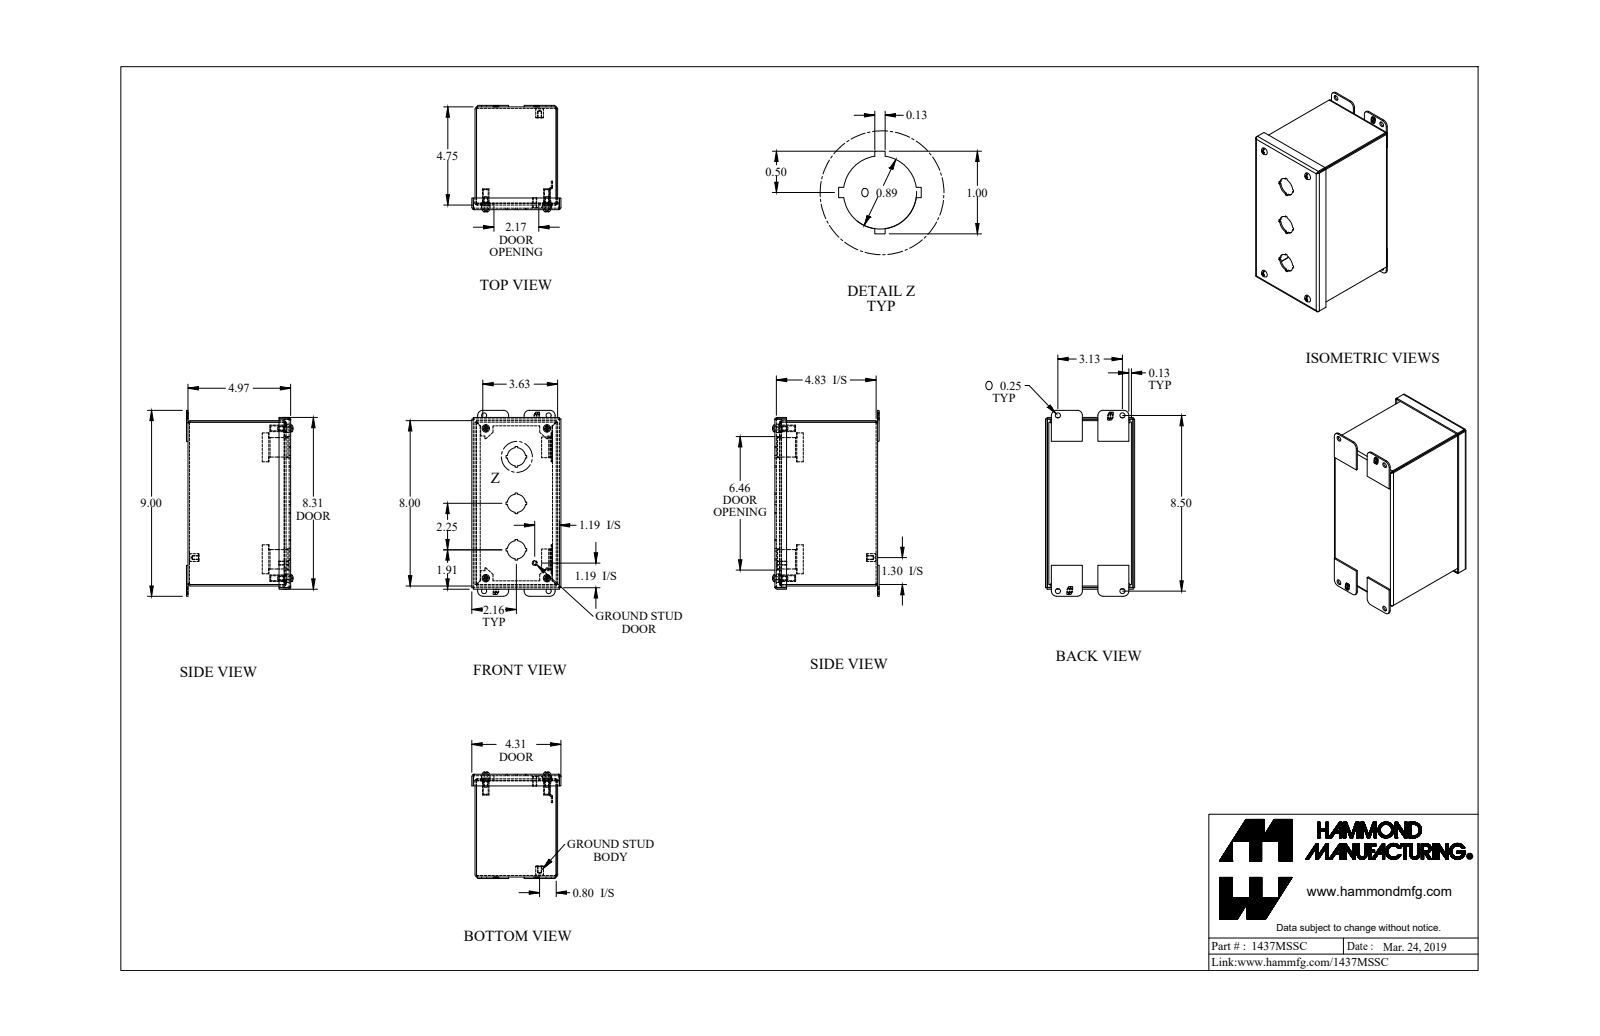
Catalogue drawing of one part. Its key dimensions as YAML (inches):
part_name: "1437MSSC_Default"
step_written_by: "SolidWorks 2019 (CONFIG_CONTROL_DESIGN)"
units: inches
bodies: {solids: 23, faces: 653, planar: 459, cylindrical: 164, other: 30}
overall_size: [9, 5.154, 4.312]
volume: 17.1
surface_area: 458
round_holes:
  - {diameter: 0.25, count: 8}
  - {diameter: 0.065, count: 4}
  - {diameter: 0.239, count: 4}
  - {diameter: 0.253, count: 4}
  - {diameter: 0.406, count: 4}
  - {diameter: 0.886, count: 3}
  - {diameter: 0.156, count: 1}
round_bosses_or_shafts:
  - {diameter: 0.19, count: 5}
  - {diameter: 0.406, count: 4}
  - {diameter: 0.315, count: 4}
  - {diameter: 0.148, count: 4}
  - {diameter: 0.375, count: 1}
  - {diameter: 0.25, count: 1}
partial_cylinders:
  - {radius: 0.036, count: 12}
  - {radius: 0.108, count: 12}
  - {radius: 0.25, count: 8}
  - {radius: 0.029, count: 4}
  - {radius: 0.086, count: 4}
  - {radius: 0.125, count: 4}
  - {radius: 0.171, count: 4}
face_to_face_distances: [0.072, 3.928, 4.9, 4.972, 3.856, 4, 7.928, 4.828, 0.156, 7.856]
hole_center_spacings: [7.25, 7.876, 0.63, 2.961, 3.107, 3.916, 6.059, 7.832]
